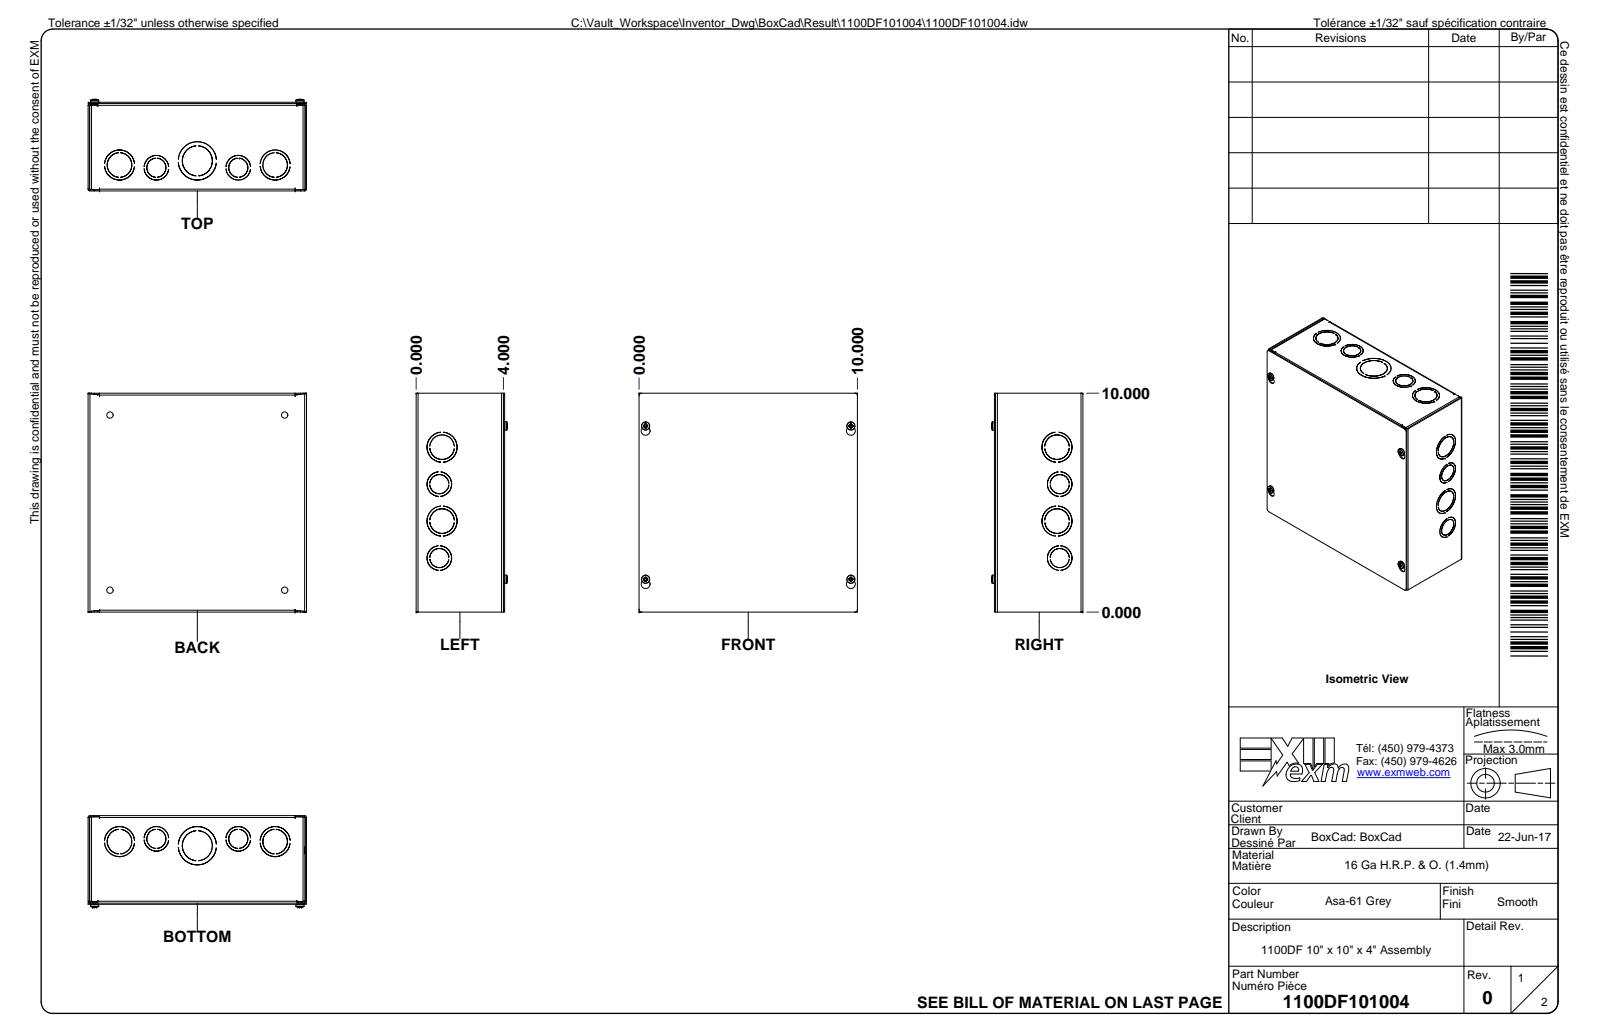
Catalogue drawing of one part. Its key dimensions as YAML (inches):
part_name: "1100DF101004; 1100DF101004B; 1100DF101004B-P; 1100DF101004C (+5 more)"
step_written_by: "Autodesk Inventor 2024 (AUTOMOTIVE_DESIGN)"
units: inches
bodies: {solids: 8, faces: 3553, planar: 2162, cylindrical: 499, other: 892}
overall_size: [10, 10, 4.183]
volume: 20.67
surface_area: 783.9
round_holes:
  - {diameter: 0.165, count: 8}
  - {diameter: 1.125, count: 8}
  - {diameter: 1.375, count: 5}
  - {diameter: 0.29, count: 4}
  - {diameter: 0.406, count: 4}
  - {diameter: 0.875, count: 4}
  - {diameter: 0.033, count: 2}
  - {diameter: 0.177, count: 2}
  - {diameter: 0.043, count: 1}
  - {diameter: 0.312, count: 1}
  - {diameter: 1.063, count: 1}
  - {diameter: 1.75, count: 1}
round_bosses_or_shafts:
  - {diameter: 1.125, count: 8}
  - {diameter: 1.375, count: 5}
  - {diameter: 0.875, count: 4}
  - {diameter: 0.374, count: 4}
  - {diameter: 0.03, count: 2}
  - {diameter: 1.75, count: 1}
  - {diameter: 1.25, count: 1}
  - {diameter: 1.142, count: 1}
partial_cylinders:
  - {radius: 0.004, count: 28}
  - {radius: 0.031, count: 14}
  - {radius: 0.086, count: 14}
  - {radius: 0.059, count: 12}
  - {radius: 0.11, count: 12}
  - {radius: 0.062, count: 4}
  - {radius: 0.094, count: 4}
  - {radius: 0.117, count: 4}
face_to_face_distances: [0.055, 9.945, 3.945, 0.053, 4, 4.053, 3.998, 10, 9.89, 3.89]
hole_center_spacings: [0.86, 7.533, 8.287, 8.714, 11.487, 7, 9.4, 11.72]
